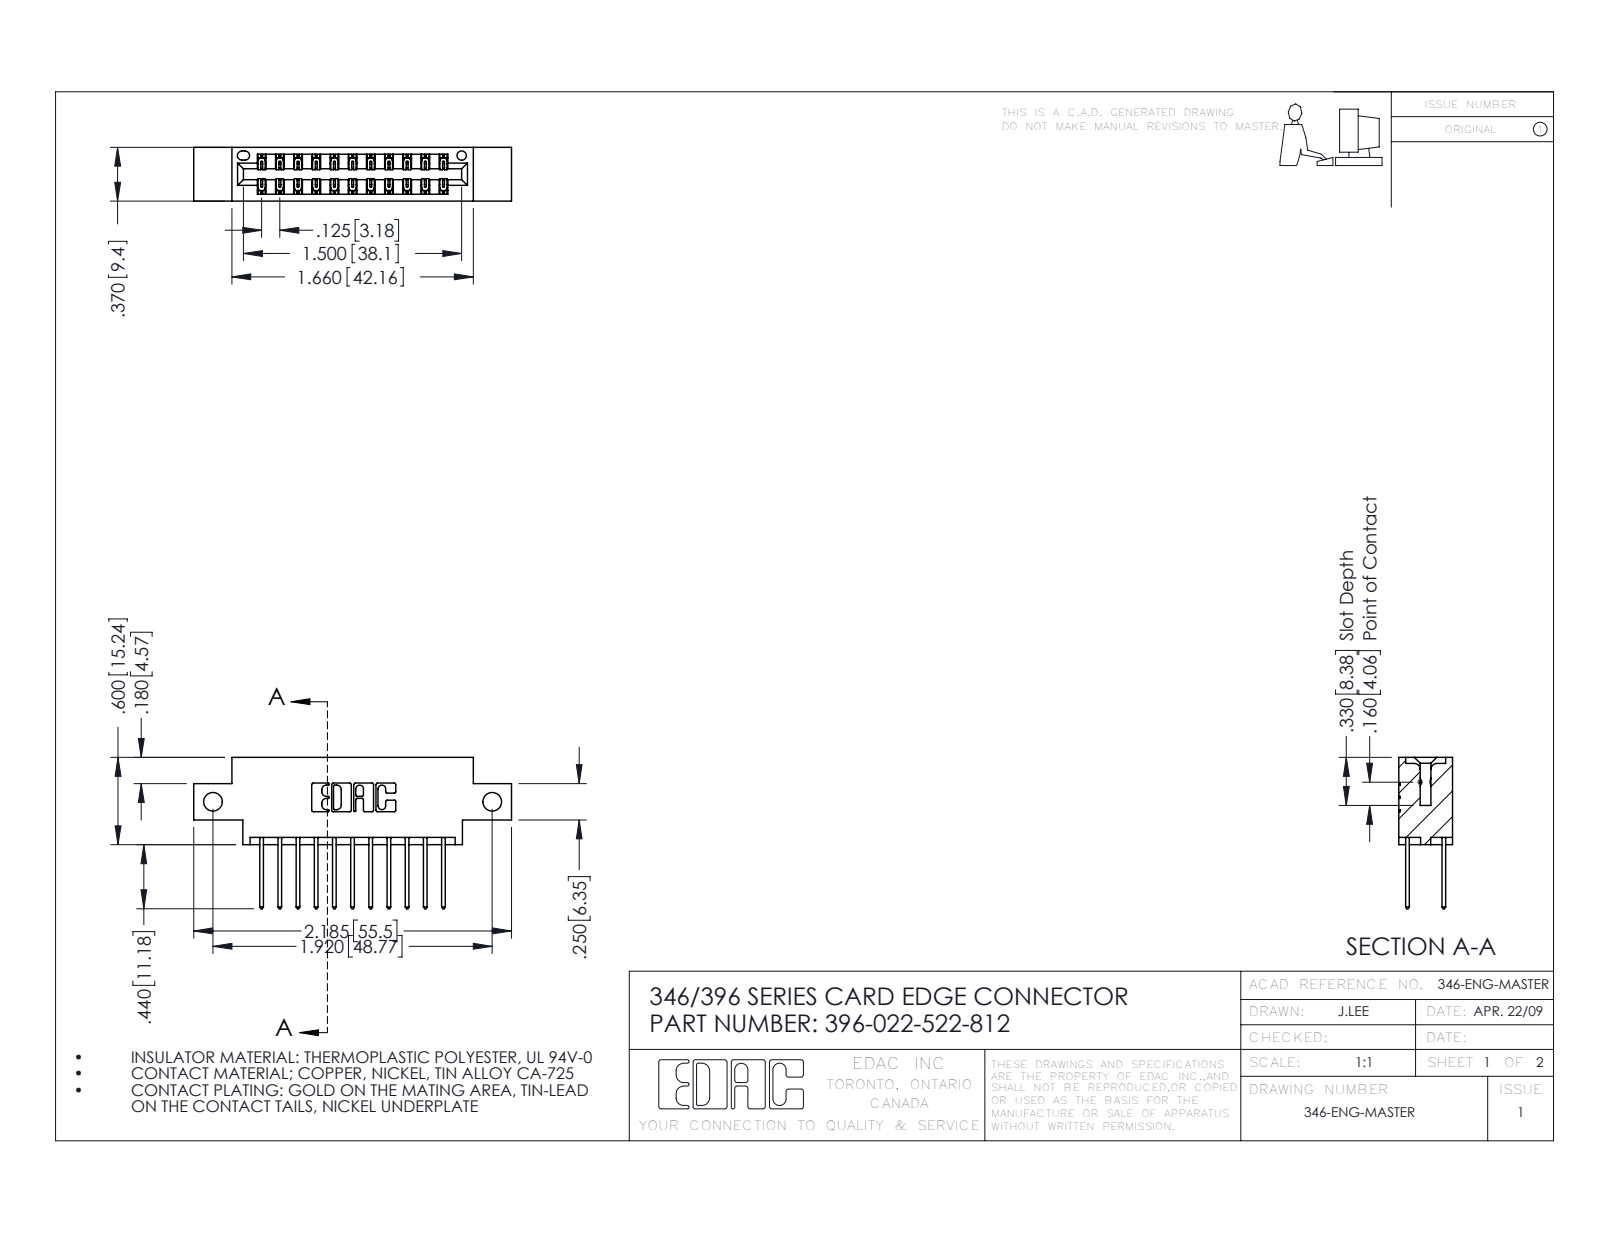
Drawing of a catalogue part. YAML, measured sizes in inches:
part_name: "345-292-001_345-293-122; 346 Part_0.170 Offset - Side Mount; 396-022-522-812"
step_written_by: "SolidWorks 2016 (CONFIG_CONTROL_DESIGN)"
units: inches
bodies: {solids: 23, faces: 1270, planar: 850, cylindrical: 420, other: 0}
overall_size: [2.185, 1.04, 0.37]
volume: 0.304
surface_area: 10.34
round_holes:
  - {diameter: 0.128, count: 2}
  - {diameter: 0.064, count: 1}
partial_cylinders:
  - {radius: 0.006, count: 33}
  - {radius: 0.01, count: 22}
  - {radius: 0.01, count: 22}
  - {radius: 0.007, count: 6}
  - {radius: 0.031, count: 6}
  - {radius: 0.026, count: 3}
  - {radius: 0.014, count: 2}
  - {radius: 0.022, count: 2}
face_to_face_distances: [0.25, 0.048, 0.322, 0.37, 0.072, 0.298, 0.025, 0.275, 0.148, 0.222]
hole_center_spacings: [1.92]
